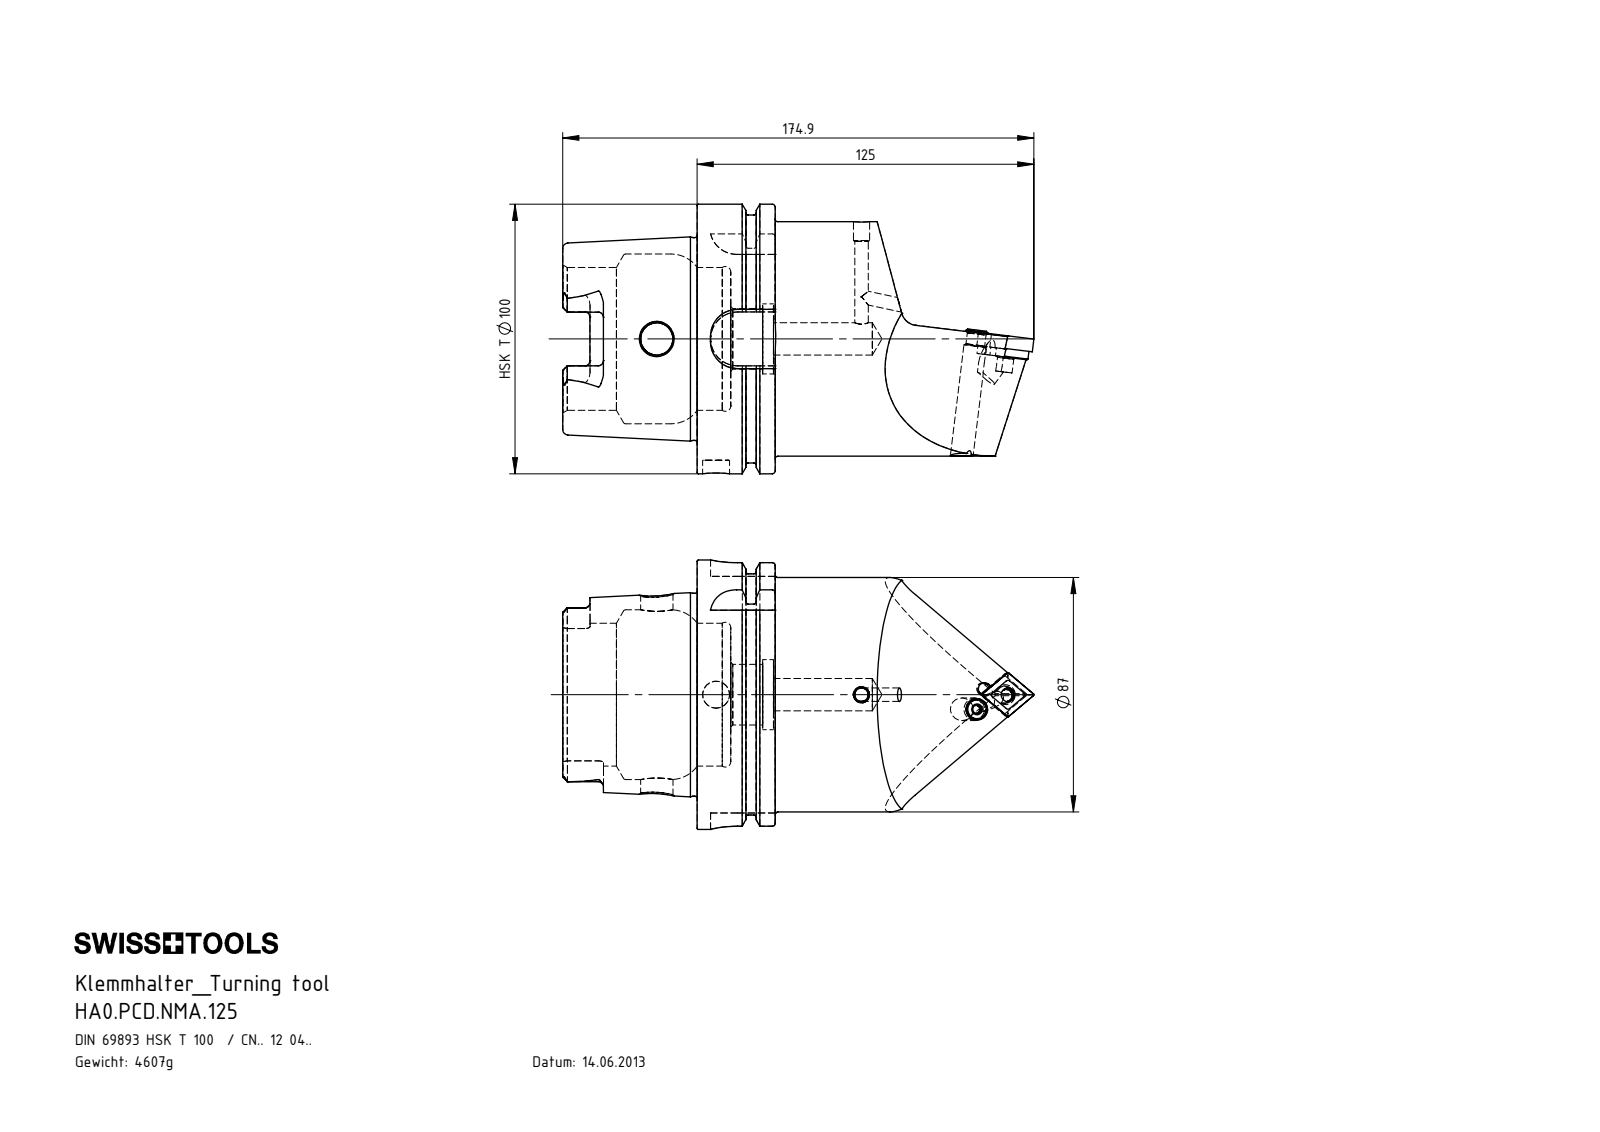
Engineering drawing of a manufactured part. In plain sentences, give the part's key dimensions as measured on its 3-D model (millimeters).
The part is named "HA0.PCD.NMA.125; WCD-ER1.101.000; WCD-ER3.101.000_A; CNMG120404 (+4 more)". Its 3-D file was written by "SolidWorks 2012 (CONFIG_CONTROL_DESIGN)". It is 8 solids with 379 faces: 116 planar, 106 cylindrical and 157 other. Overall it measures 174.9 by 100 by 100 millimeters. Its volume is 586 075 cubic millimeters and its surface area 72 007 square millimeters. Round holes: 2 of diameter 5, 2 of diameter 12, 1 of diameter 5.16, 1 of diameter 6.4, 1 of diameter 7, 1 of diameter 8.4, 1 of diameter 10, 1 of diameter 22.5, 1 of diameter 26, 1 of diameter 53, 1 of diameter 63. Round bosses or shafts: 1 of diameter 100, 1 of diameter 91.95, 1 of diameter 87, 1 of diameter 75.26, 1 of diameter 8, 1 of diameter 7.9, 1 of diameter 6.4, 1 of diameter 6. Partial cylindrical surfaces (rounded edges, fillets, slot ends): 6 of radius 1.9, 4 of radius 0.4, 4 of radius 1, 4 of radius 4.88, 4 of radius 10, 2 of radius 2.5, 1 of radius 2.1, 1 of radius 2.2. The main face-to-face distances are 12.45, 28.95, 16.5, 49.9, 62.35, 78.85, 87.8, 15.85, 0.65, 78.2. The hole center spacings are 12.8, 12.85, 54.
